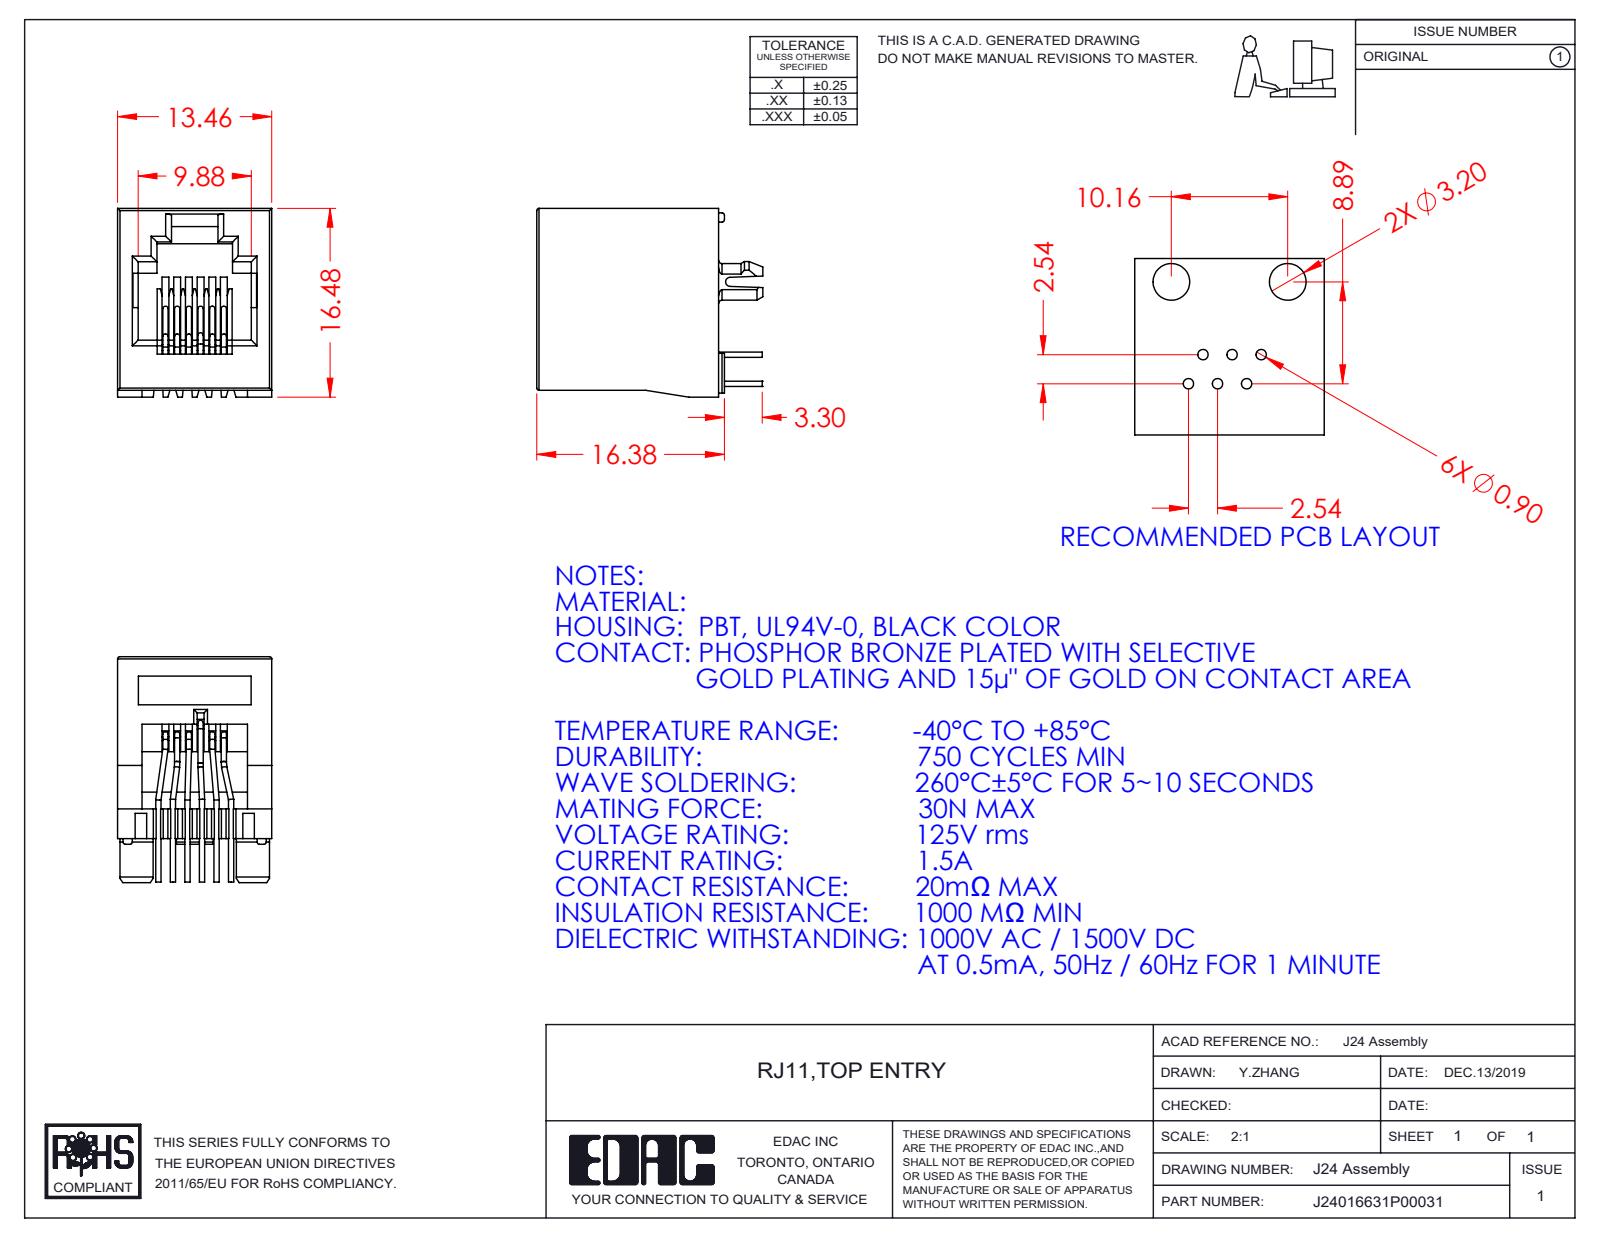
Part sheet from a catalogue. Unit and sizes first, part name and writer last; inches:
Units: inches
Overall size (bounding box): 0.777 × 0.649 × 0.53
Round holes (diameter × count): ⌀0.018 ×6, ⌀0.083 ×2
Round bosses / shafts (diameter × count): ⌀0.018 ×27
Partial cylindrical surfaces — rounded edges, fillets, slot ends (radius × count): R0.02 ×18, R0.008 ×10, R0.013 ×6, R0.013 ×6, R0.01 ×3, R0.063 ×2, R0.07 ×2, R0.016 ×1
Main face-to-face distances: 0.53, 0.04, 0.07, 0.459, 0.08, 0.024, 0.625, 0.324, 0.135, 0.395
Hole centre spacings: 0.112, 0.1, 0.18, 0.2, 0.516, 0.269, 0.4, 0.407
Volume: 0.107 in³ · Surface area: 4.557 in²
Bodies: 7 solids, 450 faces (262 planar, 152 cylindrical, 36 other)
Part name (STEP PRODUCT): RJ24016631P00071; 24 Contacts_MBB; 24 Insulator_MBB
STEP written by: SolidWorks 2016 (CONFIG_CONTROL_DESIGN)
